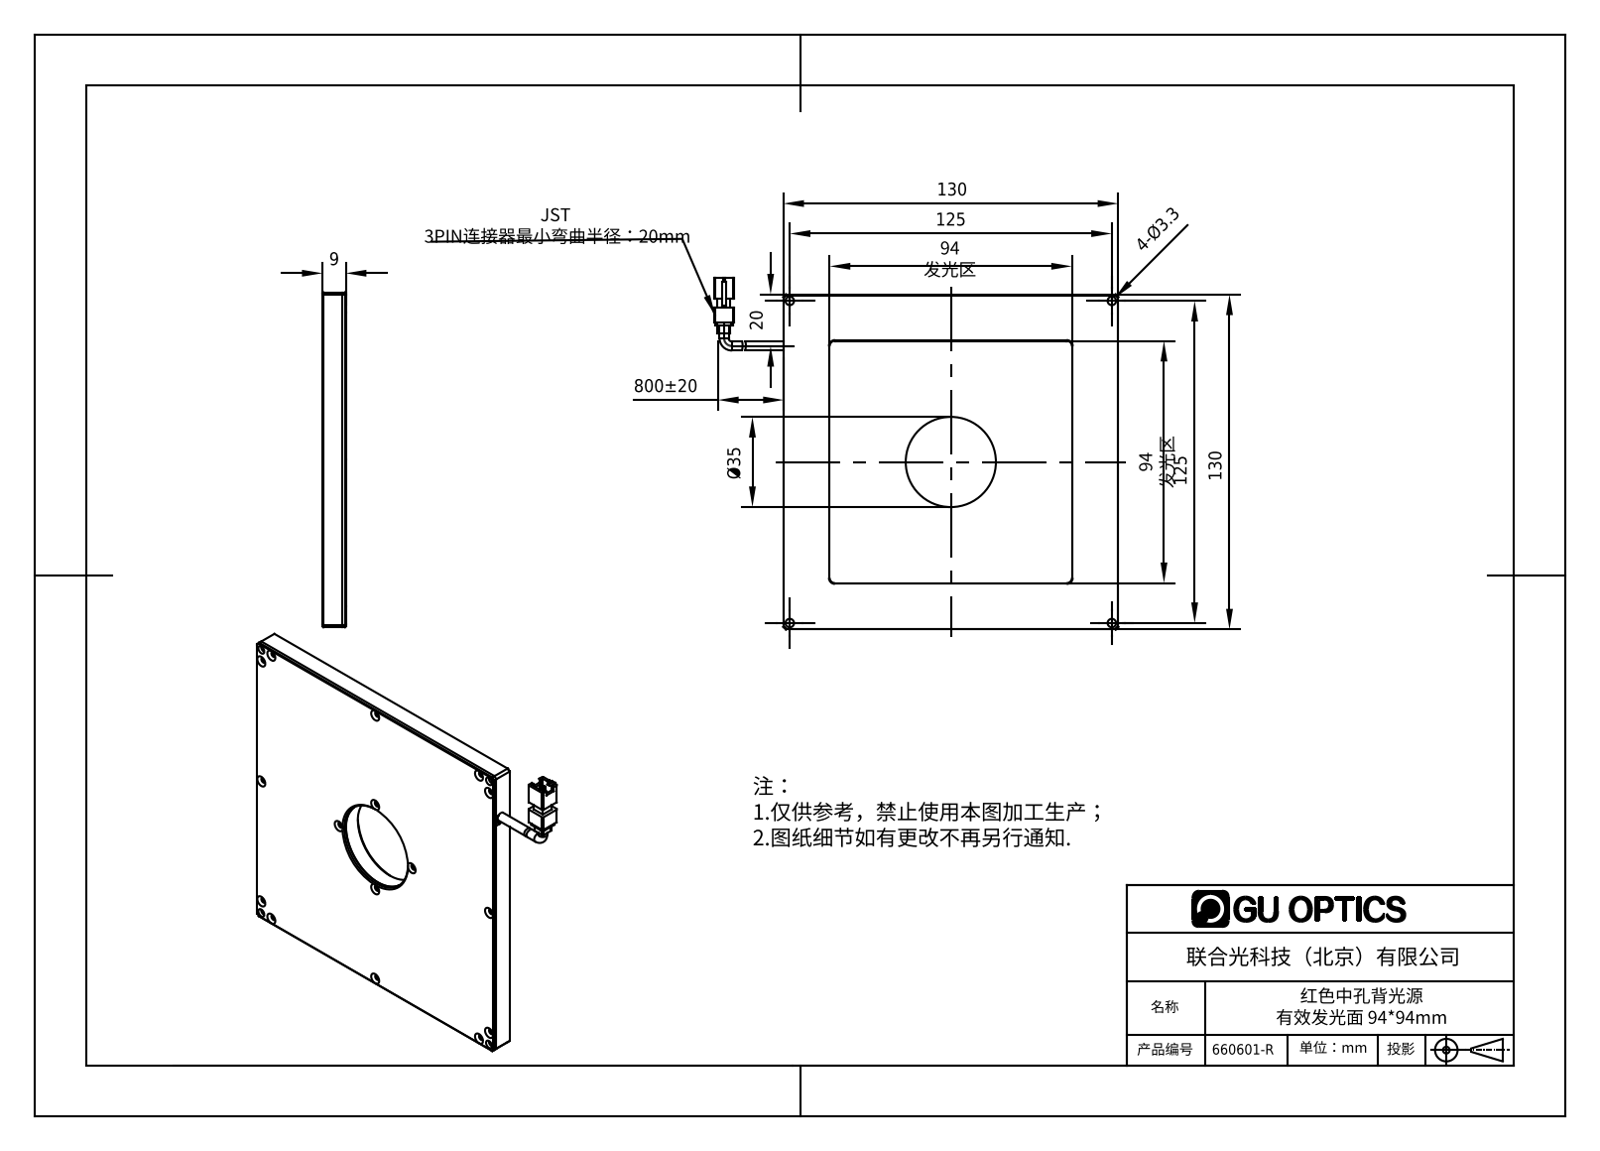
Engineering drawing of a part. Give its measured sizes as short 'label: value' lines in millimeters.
name: 660601-R
written by: SolidWorks 2016 (AUTOMOTIVE_DESIGN)
unit: mm
bodies: 6 solids, 474 faces (191 planar, 148 cylindrical, 135 other)
size: 157 × 136.5 × 10
volume: 93 254 mm³; area: 85 777 mm²
holes: 16× ⌀1.6, 12× ⌀2, 12× ⌀2.2, 4× ⌀2.4, 4× ⌀3.3, 1× ⌀35, 1× ⌀43
bosses: 2× ⌀3.5, 1× ⌀45.8, 1× ⌀42.8
rounds: 8× R0.5, 6× R1.5, 4× R1, 4× R2, 1× R1.6
face distances: 4, 6.5, 1.5, 8, 2.5, 9, 5, 1, 7.5, 126
hole spacings: 62.5, 125, 5.5, 57, 62.74, 65.62, 71.1, 72.63
